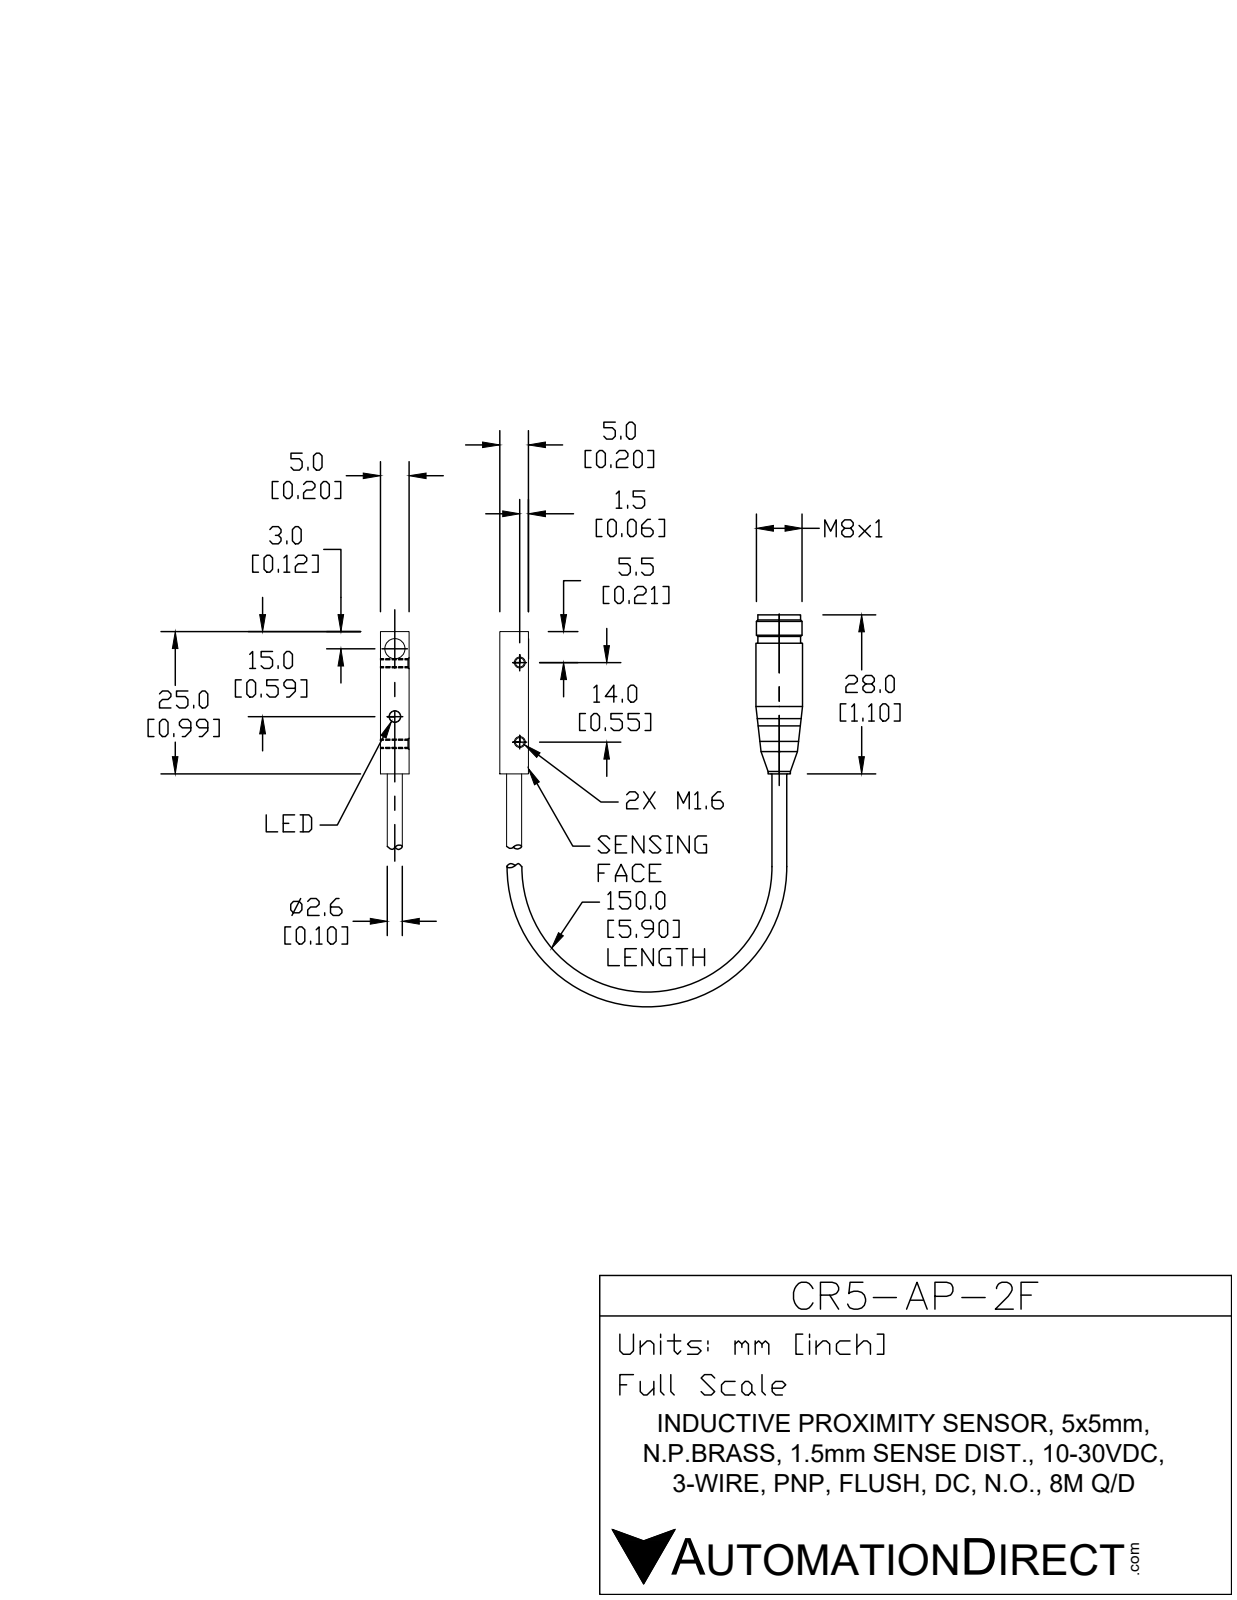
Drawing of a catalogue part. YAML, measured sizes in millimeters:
part_name: "CR5-AP-2F"
step_written_by: "SolidWorks 2017 (AUTOMOTIVE_DESIGN)"
units: millimeters
bodies: {solids: 2, faces: 359, planar: 127, cylindrical: 84, other: 148}
overall_size: [94.8, 10, 10]
volume: 2590
surface_area: 2157
round_holes:
  - {diameter: 1.2, count: 2}
  - {diameter: 5.8, count: 1}
round_bosses_or_shafts:
  - {diameter: 1, count: 3}
  - {diameter: 9.8, count: 1}
  - {diameter: 8, count: 1}
  - {diameter: 7.5, count: 1}
  - {diameter: 6.9, count: 1}
  - {diameter: 6.5, count: 1}
  - {diameter: 2.6, count: 1}
partial_cylinders:
  - {radius: 0.2, count: 8}
  - {radius: 5, count: 1}
face_to_face_distances: [5, 0.9, 1.8, 2.7, 60, 6.5, 29.8, 89.8, 64.8, 35]
hole_center_spacings: [14]
